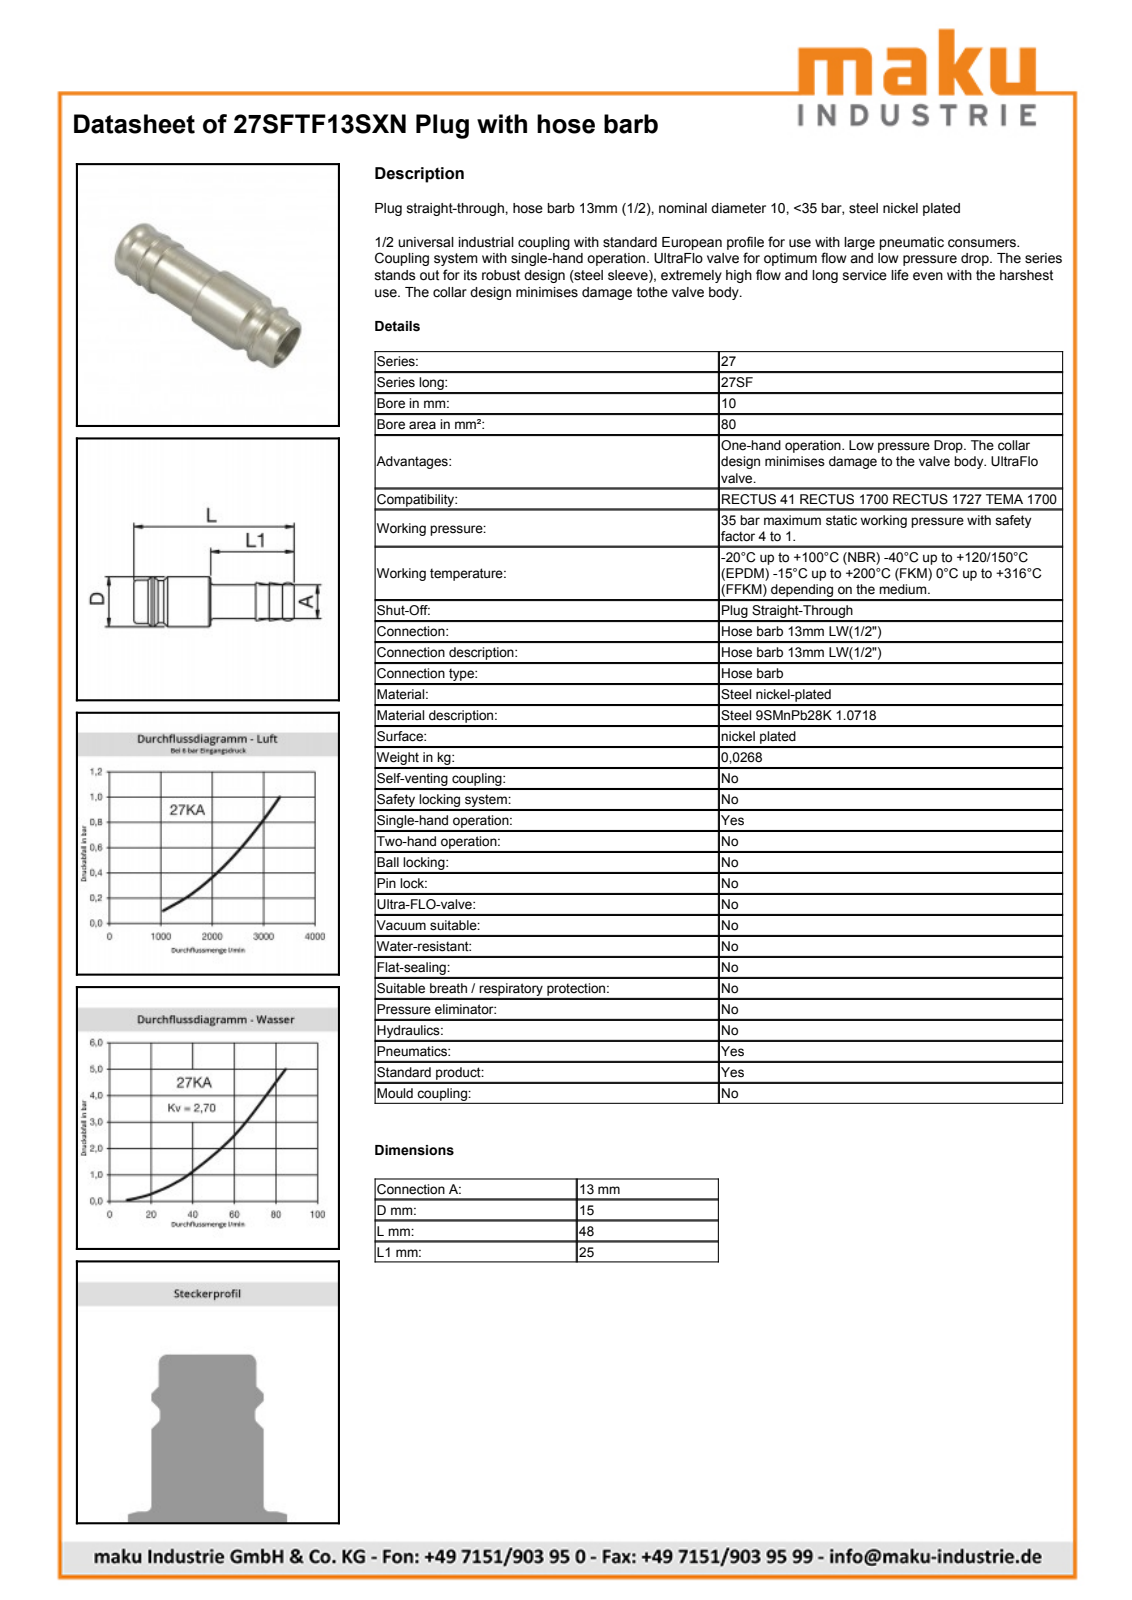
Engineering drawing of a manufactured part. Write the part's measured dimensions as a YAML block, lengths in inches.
part_name: "D106658"
step_written_by: "Autodesk Inventor 2013 (AUTOMOTIVE_DESIGN)"
units: inches
bodies: {solids: 1, faces: 25, planar: 4, cylindrical: 6, other: 15}
overall_size: [1.89, 0.591, 0.591]
volume: 0.213
surface_area: 5.899
round_holes:
  - {diameter: 0.394, count: 1}
round_bosses_or_shafts:
  - {diameter: 0.591, count: 1}
  - {diameter: 0.516, count: 1}
  - {diameter: 0.512, count: 1}
  - {diameter: 0.498, count: 1}
face_to_face_distances: [1.89, 1.437, 0.453, 1.594, 0.157, 0.295]
